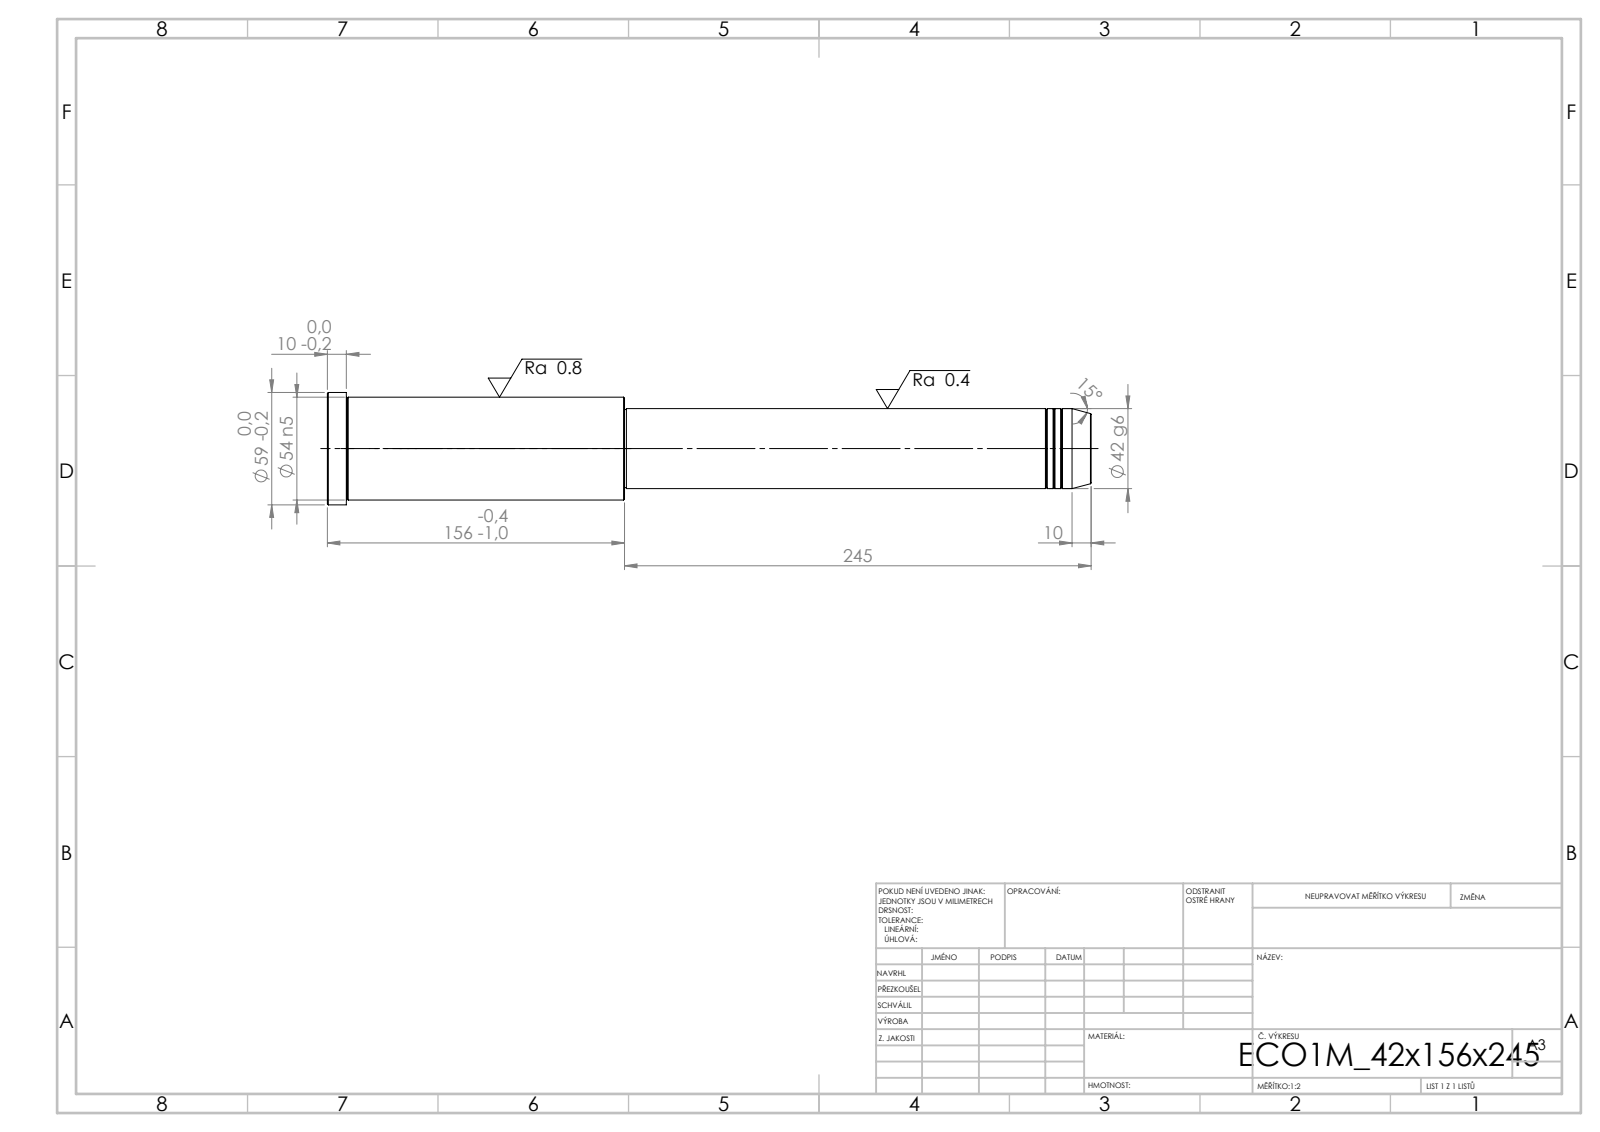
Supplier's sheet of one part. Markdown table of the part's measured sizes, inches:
| quantity | value |
| --- | --- |
| STEP written by | SolidWorks 2019 (CONFIG_CONTROL_DESIGN) |
| units | inches |
| bodies | 1 solid, 43 faces (5 planar, 14 cylindrical, 24 other) |
| overall size | 15.787 × 2.323 × 2.323 |
| volume | 42.66 in³ |
| surface area | 99.77 in² |
| round bosses / shafts (diameter × count) | 2.323 × 1, 2.126 × 1, 1.654 × 1, 1.614 × 1 |
| main face-to-face distances | 15.787, 9.646, 6.142, 15.394, 5.748, 0.394, 9.606, 0.039, 5.787, 6.181 |
